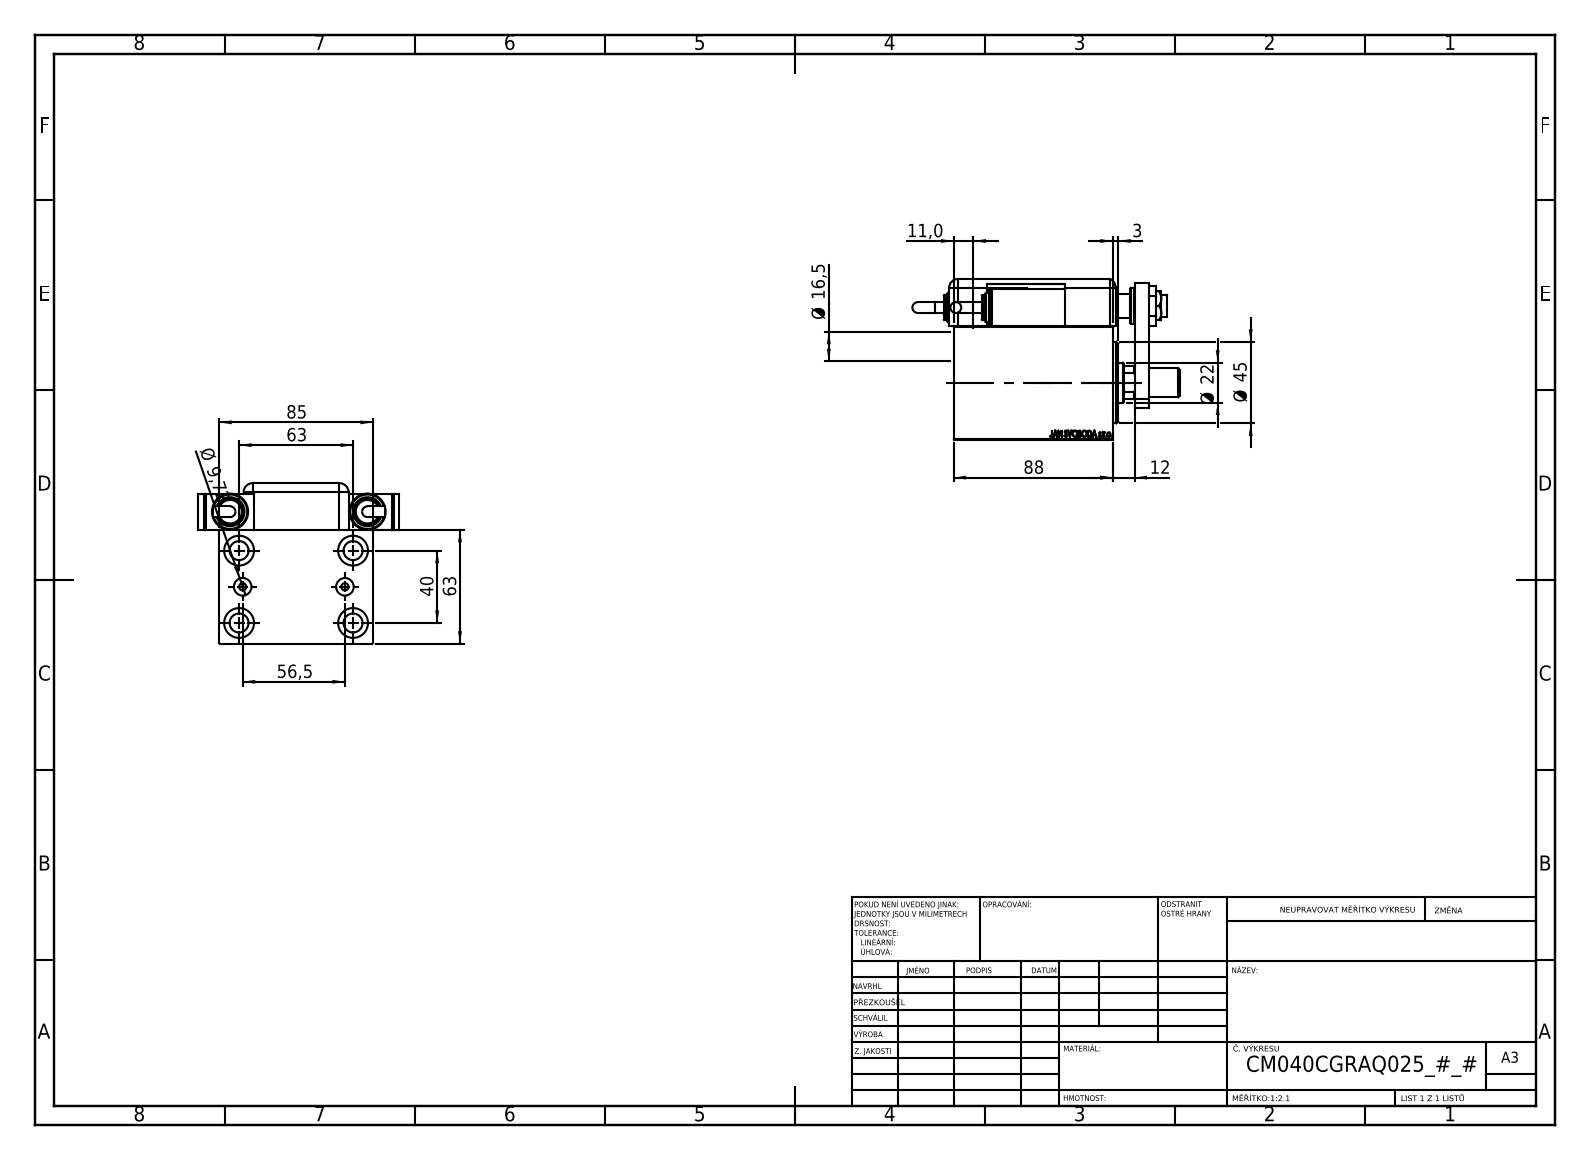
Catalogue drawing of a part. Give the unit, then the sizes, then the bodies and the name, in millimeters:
Units: millimetres
Overall size (bounding box): 147.76 × 111 × 88.8
Round holes (diameter × count): ⌀4 ×4, ⌀10.5 ×4, ⌀16.5 ×4, ⌀8 ×2, ⌀9.72 ×2, ⌀14 ×2, ⌀12 ×1, ⌀12.5 ×1, ⌀13 ×1, ⌀22 ×1, ⌀25.5 ×1, ⌀40 ×1
Round bosses / shafts (diameter × count): ⌀20 ×3, ⌀16 ×3, ⌀14 ×3, ⌀6 ×2
Partial cylindrical surfaces — rounded edges, fillets, slot ends (radius × count): R5 ×9, R10 ×1, R10.5 ×1
Main face-to-face distances: 3, 63, 13.5, 85, 12, 83, 10.5, 88, 20, 1.5
Hole centre spacings: 37.31, 20.1, 20.5, 36.79, 37.86, 38.71, 40, 61.82
Volume: 547 775 mm³ · Surface area: 130 701 mm²
Bodies: 14 solids, 1256 faces (618 planar, 115 cylindrical, 523 other)
Part name (STEP PRODUCT): V450CM_C_VCP; V450CM_C_Body; TYC; KRYT (+8 more)
STEP written by: SolidWorks 2019 (CONFIG_CONTROL_DESIGN)
